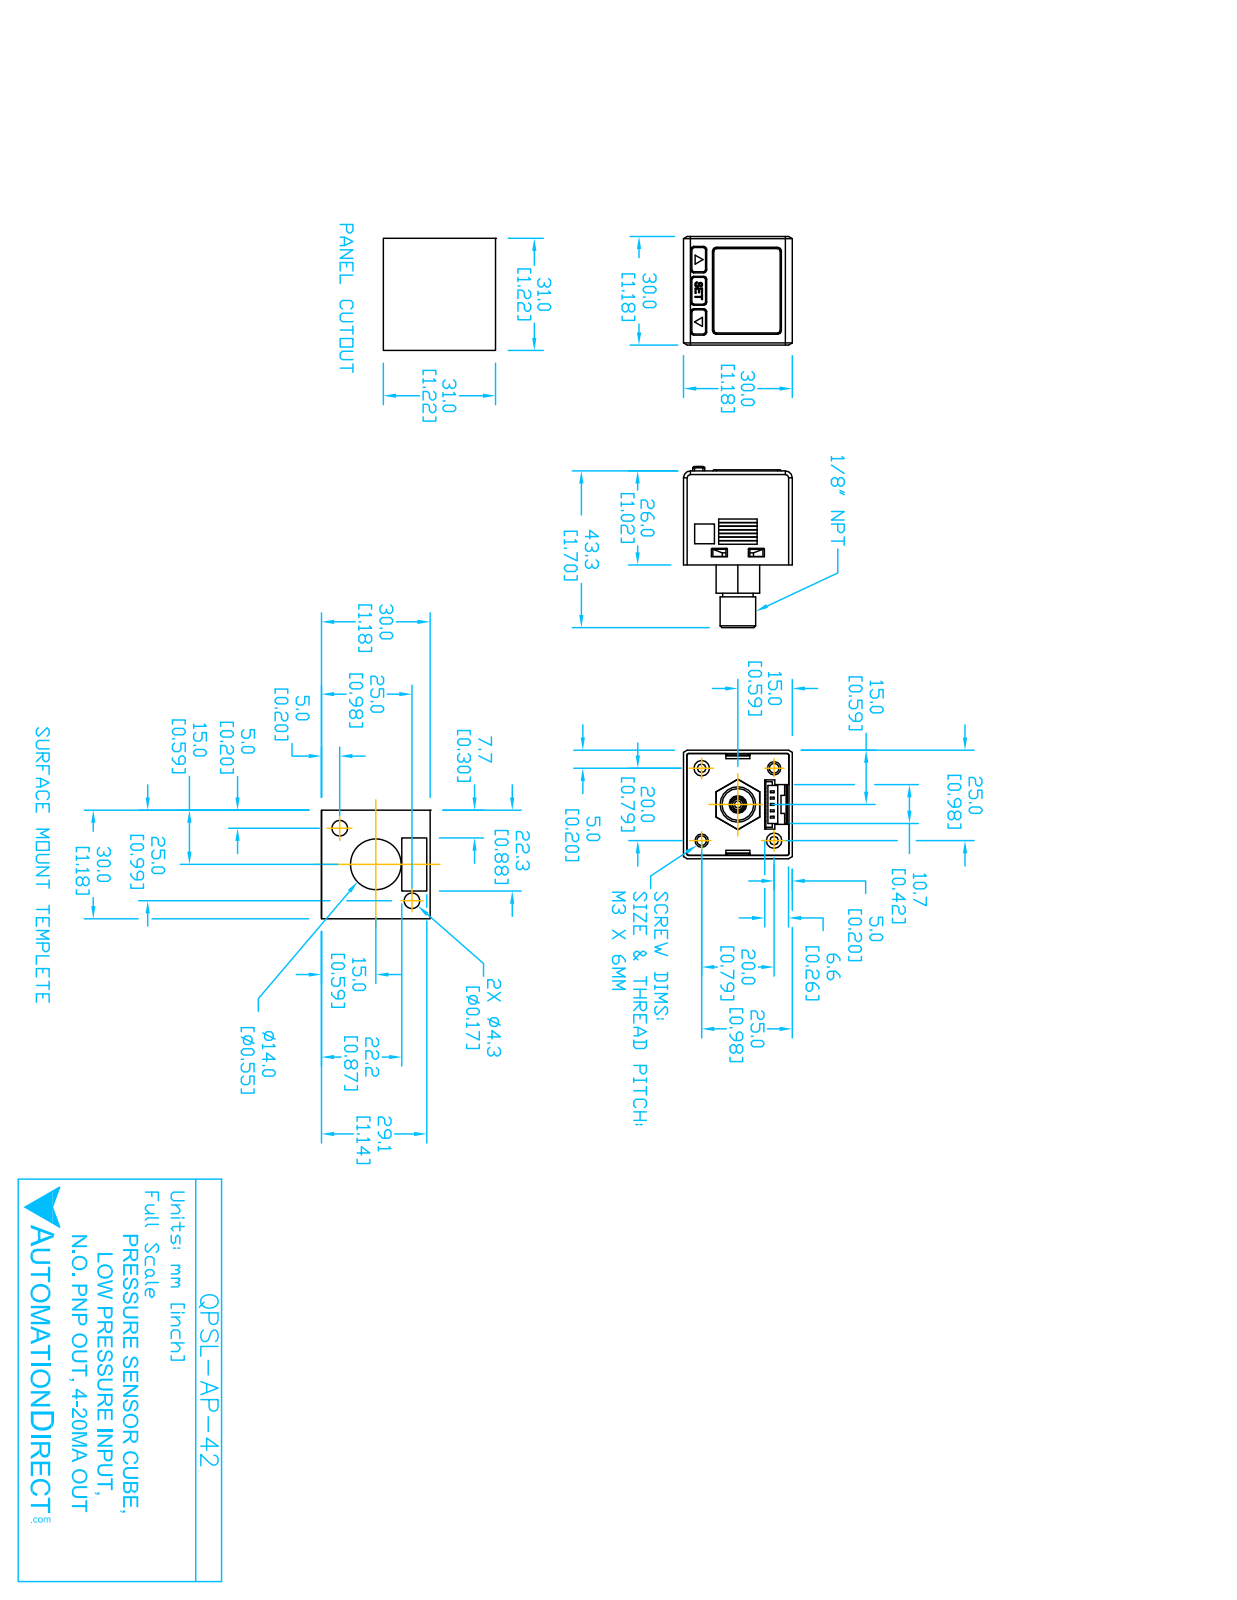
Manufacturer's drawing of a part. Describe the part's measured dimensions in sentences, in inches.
The part is named "QPSL-AP-42". Its 3-D file was written by "SolidWorks 2014 (AUTOMOTIVE_DESIGN)". It is 1 solid with 386 faces: 296 planar, 62 cylindrical and 28 other. Overall it measures 1.806 by 1.18 by 1.18 inches. Its volume is 1.496 cubic inches and its surface area 10.41 square inches. Round holes: 2 of diameter 0.105, 2 of diameter 0.12, 2 of diameter 0.19, 1 of diameter 0.165. Round bosses or shafts: 1 of diameter 0.375, 1 of diameter 0.32. Partial cylindrical surfaces (rounded edges, fillets, slot ends): 16 of radius 0.02, 8 of radius 0.015, 2 of radius 0.06. The main face-to-face distances are 1.18, 1.041, 1.04, 0.03, 0.04, 0.476, 0.052, 0.564, 0.061, 0.352. The hole center spacings are 0.552, 0.78, 1.104.
